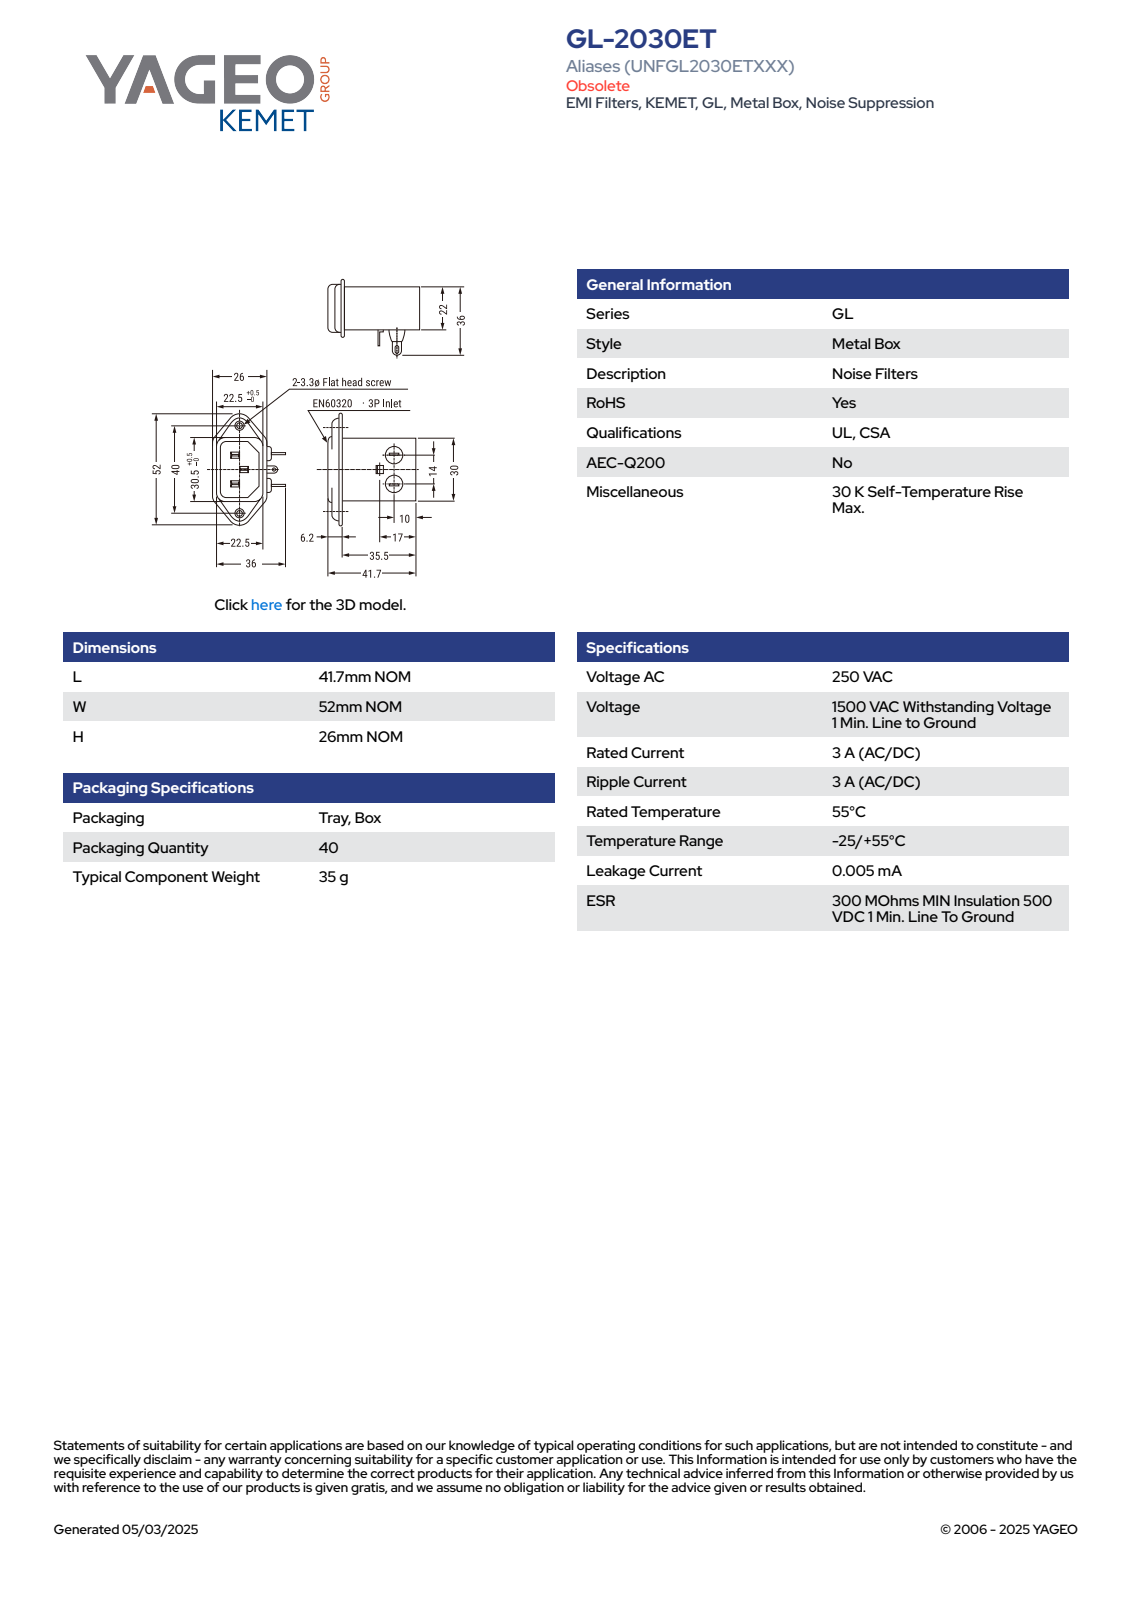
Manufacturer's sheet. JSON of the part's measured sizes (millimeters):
{"part_name": "ENF_KGLE_L41.7W52H26", "step_written_by": "SolidWorks 2014 (AUTOMOTIVE_DESIGN)", "units": "millimeters", "bodies": {"solids": 1, "faces": 188, "planar": 117, "cylindrical": 59, "other": 12}, "overall_size": [52, 41.7, 38], "volume_mm3": 26842, "surface_area_mm2": 7324, "round_holes": [[3.3, 2], [1.75, 1]], "round_bosses_or_shafts": [[6, 2]], "partial_cylinders_radius": [[1, 26], [1.5, 6], [3, 4], [0.75, 2], [2, 2]], "face_to_face_distances": [22, 2, 30, 37.5, 35.5, 0.5, 1.5, 22.5, 20.5, 21], "hole_center_spacings": [25.99, 40]}
